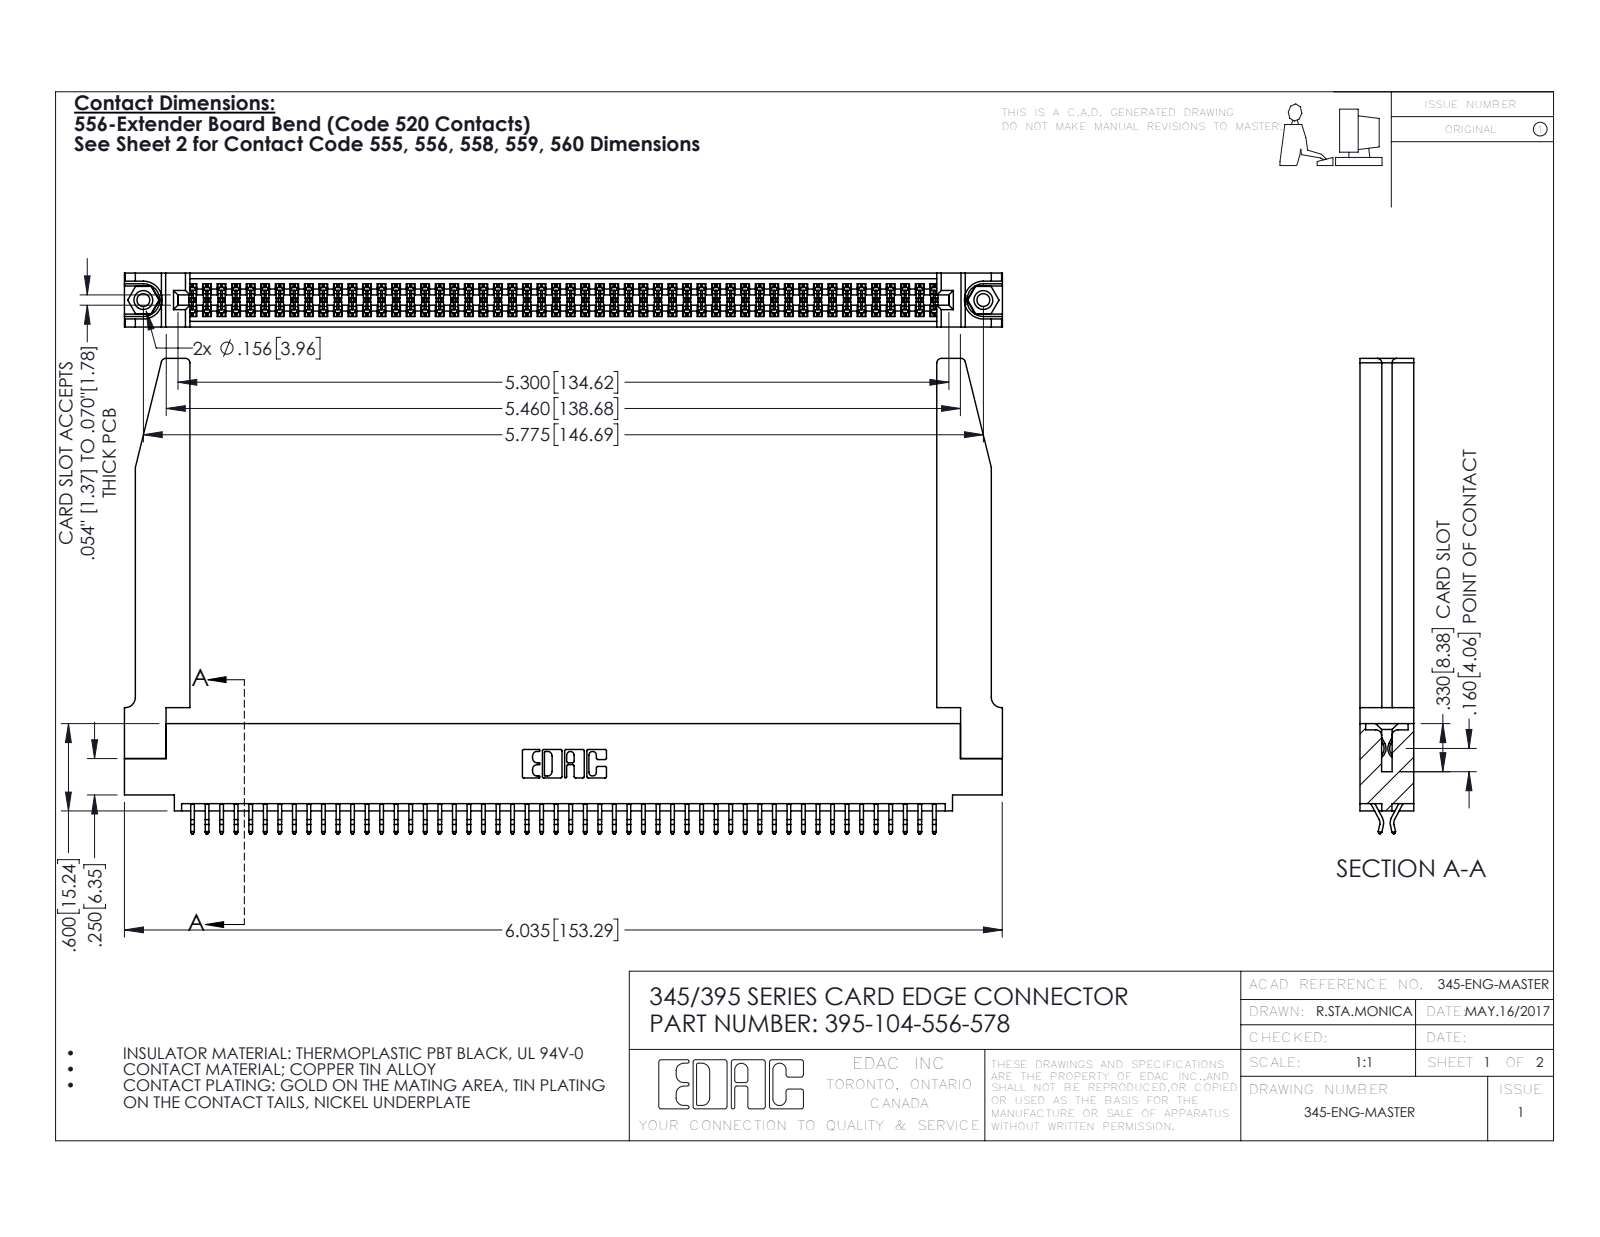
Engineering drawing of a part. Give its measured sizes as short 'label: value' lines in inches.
name: 345-292-001_556 Tail; 345-220-078_345-220-078; 395-104-556-578; 345-250-001_345-250-001-102 (+1 more)
written by: SolidWorks 2016 (CONFIG_CONTROL_DESIGN)
unit: in
bodies: 109 solids, 6188 faces (4074 planar, 2062 cylindrical, 52 other)
size: 6.036 × 3.267 × 0.37
volume: 1.384 in³; area: 45.06 in²
holes: 2× ⌀0.089, 2× ⌀0.125, 2× ⌀0.156, 1× ⌀0.064
bosses: 2× ⌀0.155
rounds: 156× R0.006, 22× R0.01, 8× R0.03, 6× R0.007, 6× R0.031, 3× R0.026, 2× R0.01, 2× R0.014
face distances: 0.072, 0.37, 0.298, 0.025, 0.098, 0.272, 0.2, 0.225, 0.175, 0.15
hole spacings: 0.27, 5.539, 5.775
